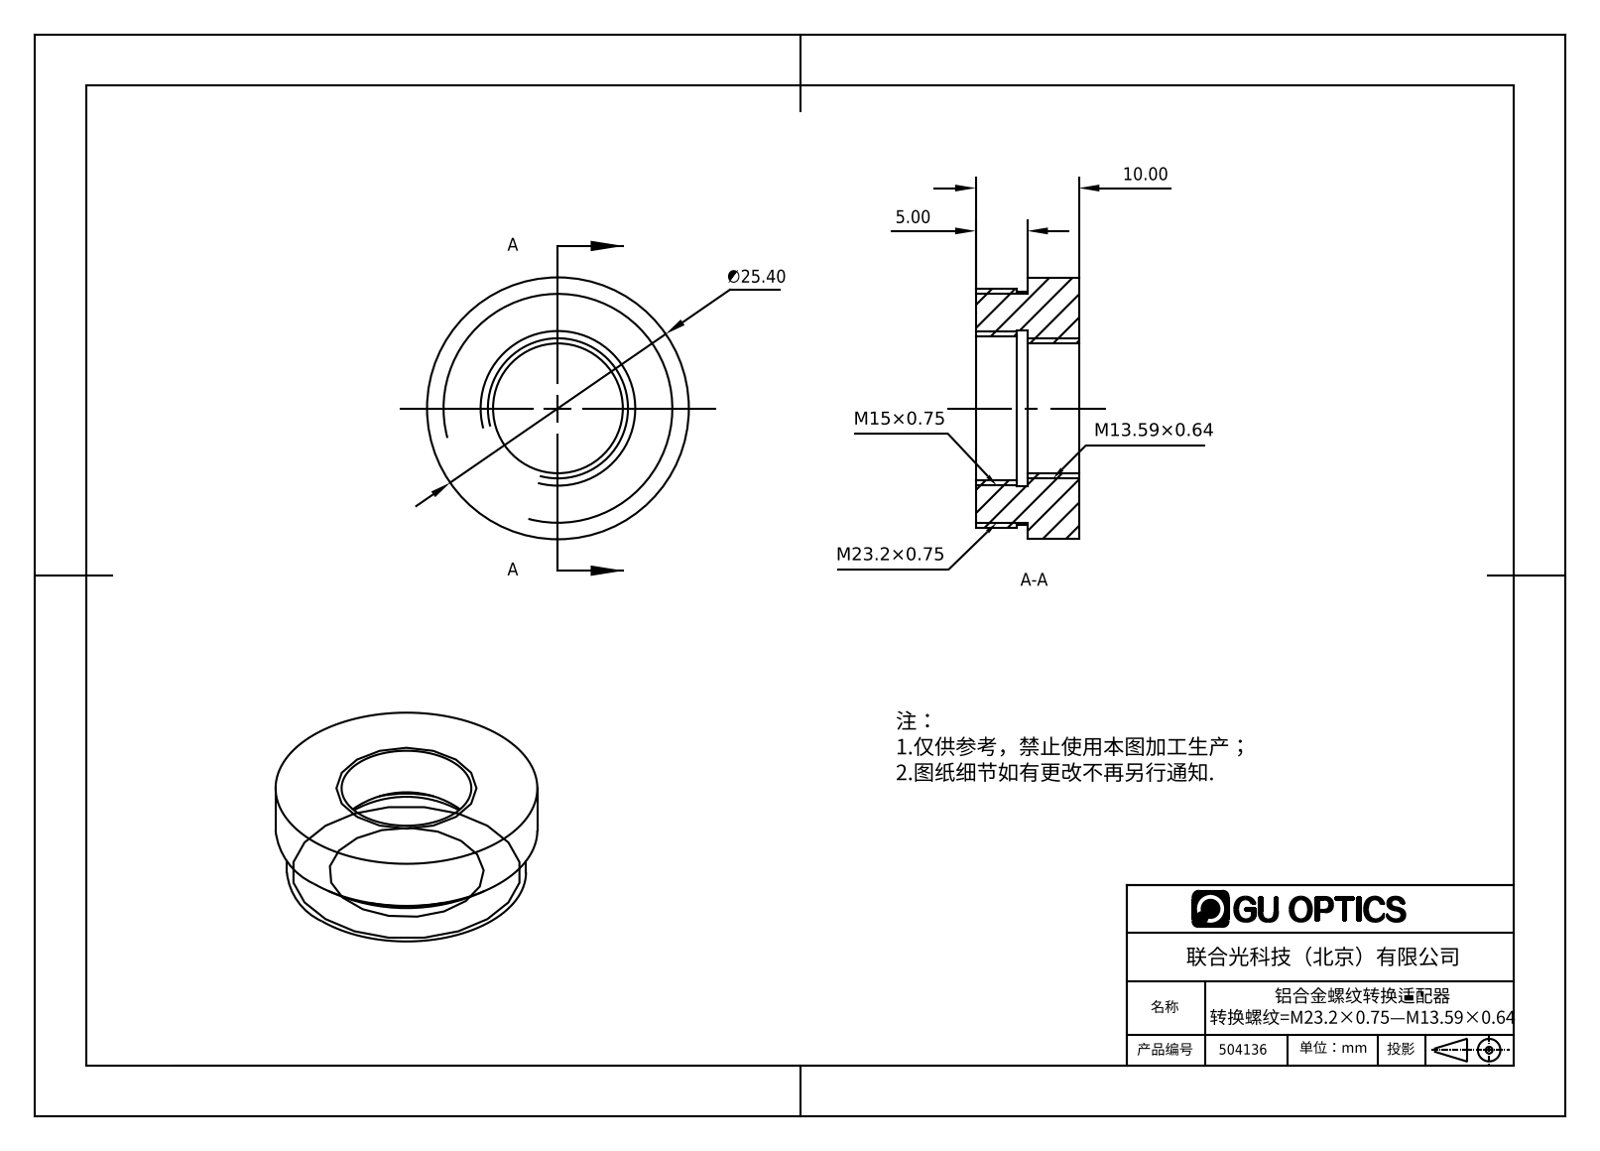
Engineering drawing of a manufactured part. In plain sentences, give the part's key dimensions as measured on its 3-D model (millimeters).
The part is named "504136". Its 3-D file was written by "SolidWorks 2016 (AUTOMOTIVE_DESIGN)". It is 1 solid with 18 faces: 6 planar, 12 cylindrical and 0 other. Overall it measures 25.4 by 25.4 by 10 millimeters. Its volume is 3 210 cubic millimeters and its surface area 2 039 square millimeters. Round holes: 1 of diameter 12.59, 1 of diameter 14, 1 of diameter 15.2. Round bosses or shafts: 1 of diameter 25.4, 1 of diameter 23.2, 1 of diameter 22.7. The main face-to-face distances are 5, 10, 4, 1, 6.
